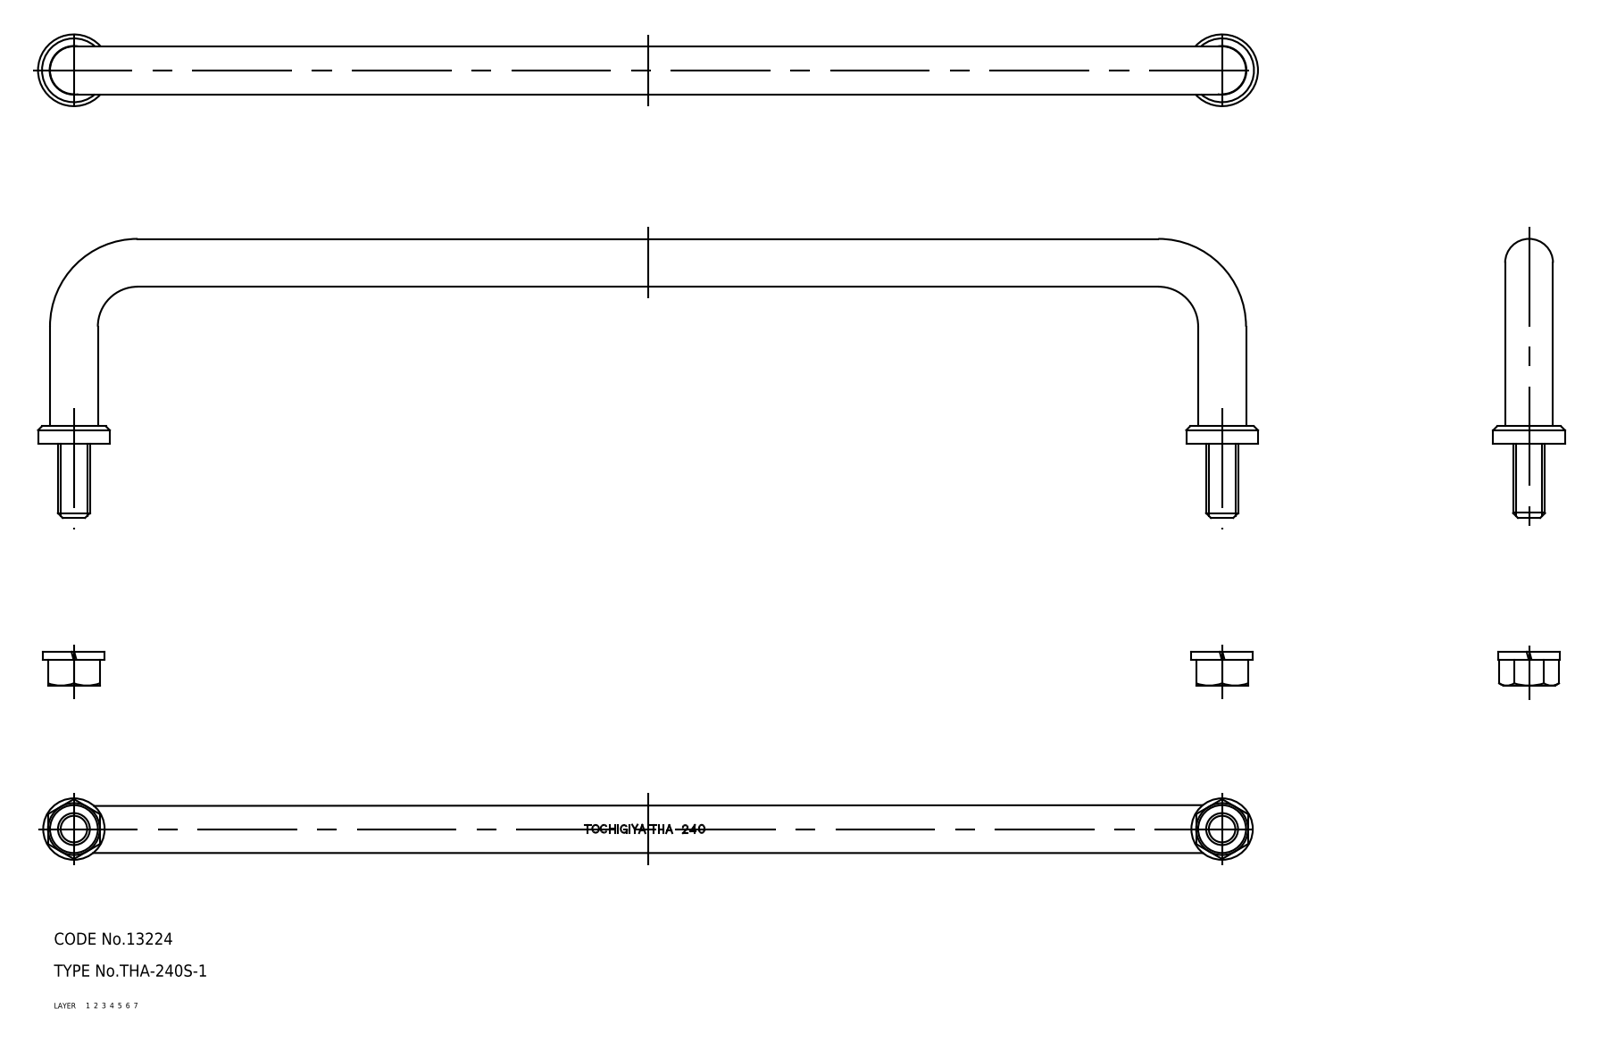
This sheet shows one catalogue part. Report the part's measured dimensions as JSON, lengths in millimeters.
{"part_name": "facing ring; nut; washer; pull (+1 more)", "step_written_by": "CADfix (AUTOMOTIVE_DESIGN)", "units": "millimeters", "bodies": {"solids": 7, "faces": 86, "planar": 0, "cylindrical": 0, "other": 86}, "overall_size": [306, 70, 18], "volume_mm3": 46173, "surface_area_mm2": 18522}
